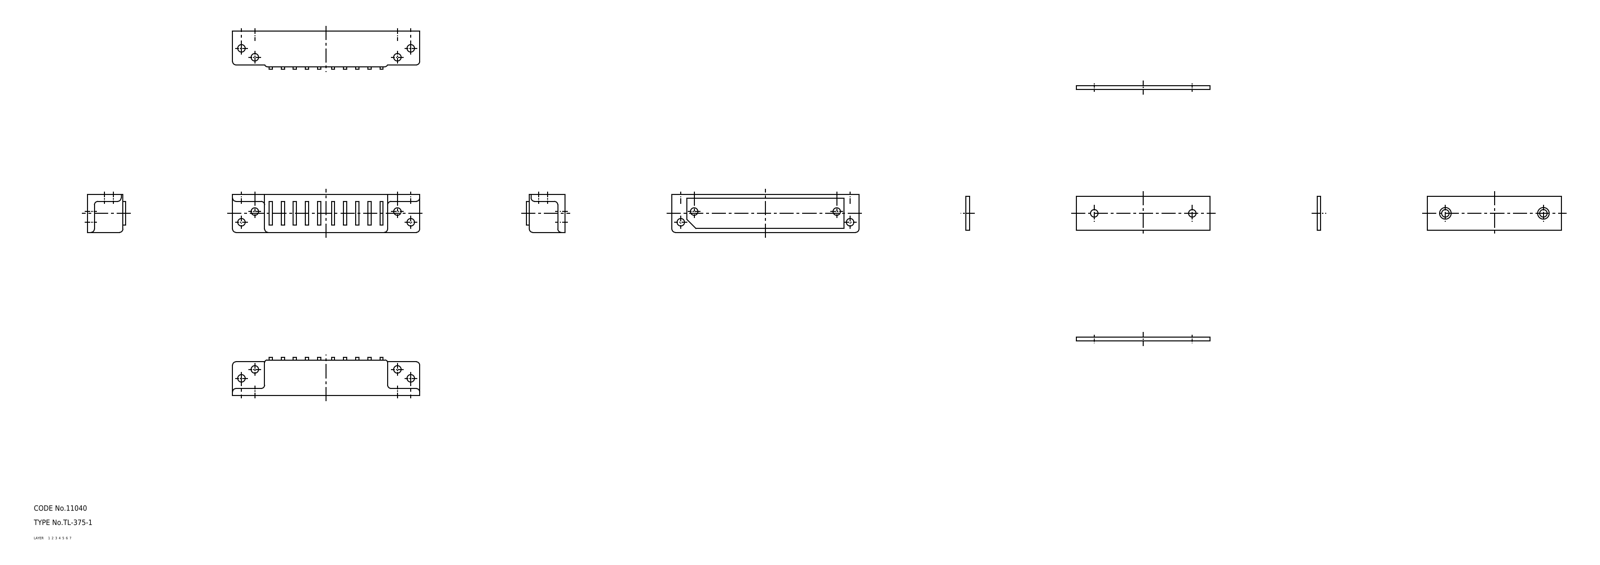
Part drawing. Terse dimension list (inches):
name: 67116911; 67116924; 67116937; 67116950 (+8 more)
written by: CADfix (AUTOMOTIVE_DESIGN)
unit: in
bodies: 12 solids, 205 faces (0 planar, 0 cylindrical, 205 other)
size: 4.134 × 2.047 × 0.843
volume: 2.274 in³; area: 35.92 in²
